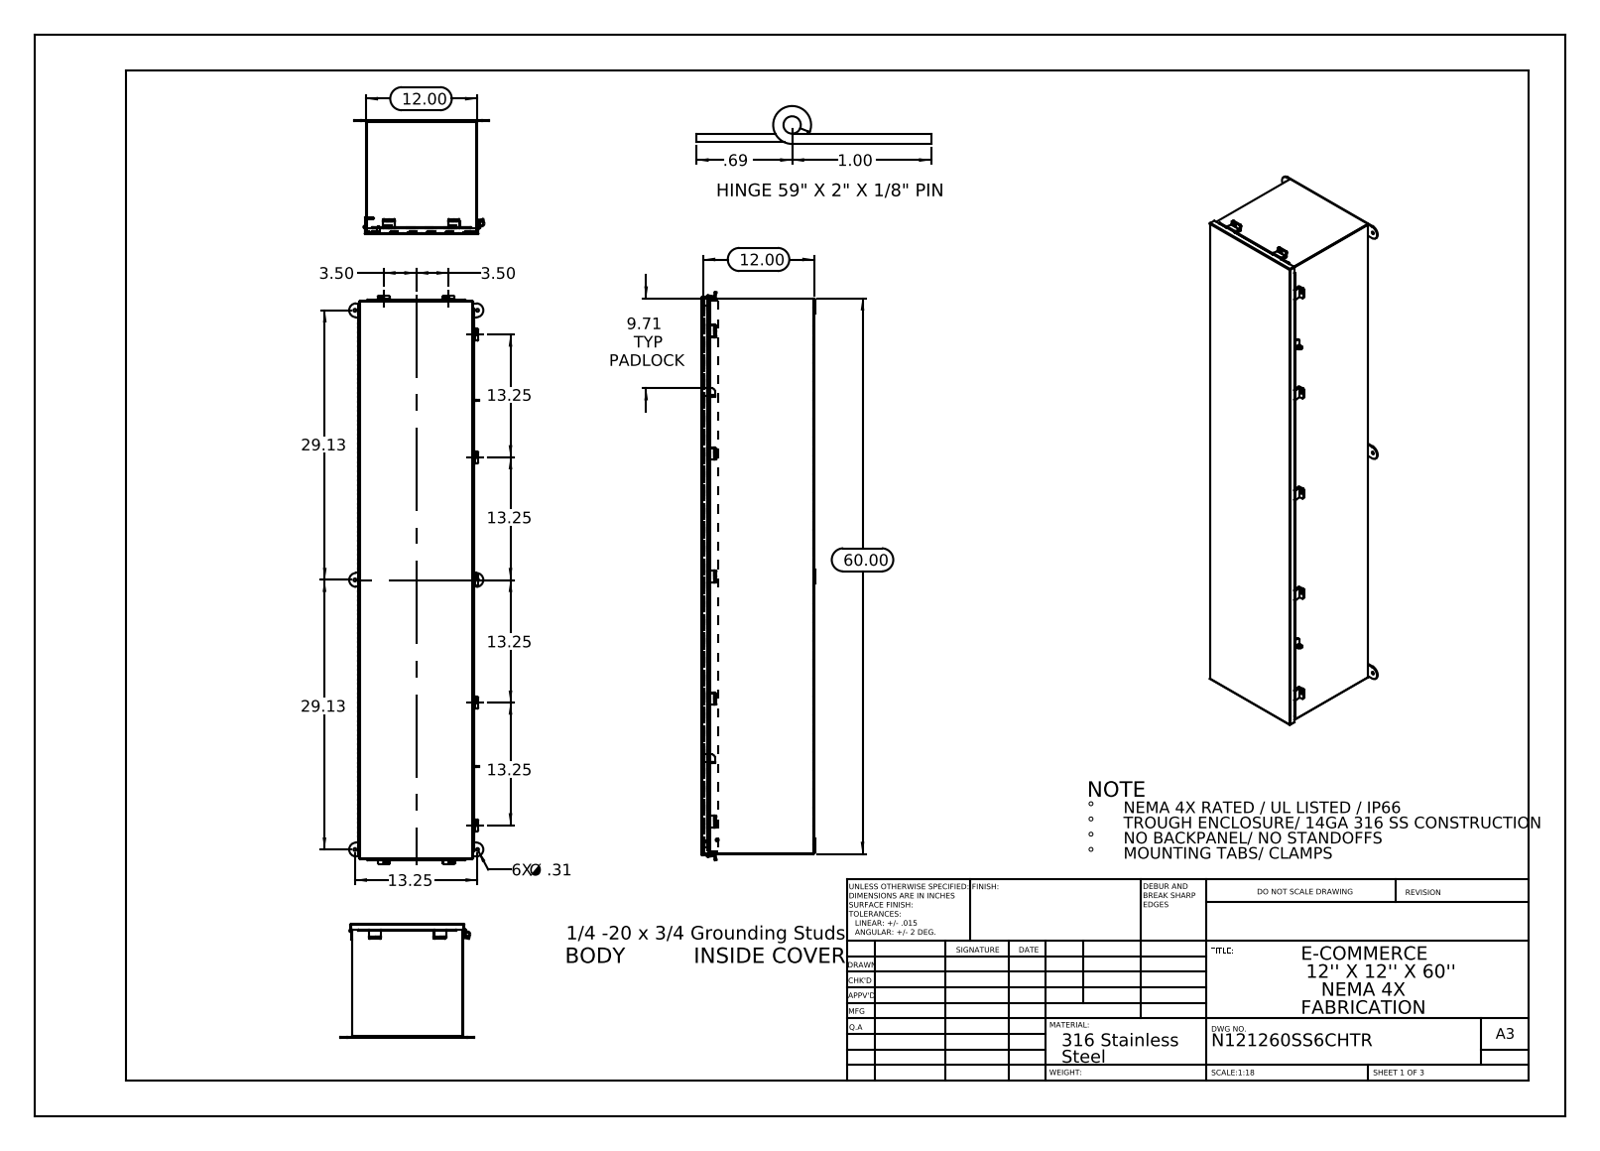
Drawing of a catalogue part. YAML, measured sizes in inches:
part_name: "N121260SSCHTR HW-CD-S-25020-034; N121260SSCHTR JIC Cover Clamp; N121260SSCHTR JIC Mounting Bracket; HW-CLH-JH-20154 (+8 more)"
step_written_by: "SolidWorks 2013 (CONFIG_CONTROL_DESIGN)"
units: inches
bodies: {solids: 31, faces: 1773, planar: 1066, cylindrical: 687, other: 20}
overall_size: [61.407, 14.5, 12.337]
volume: 266.4
surface_area: 7123
round_holes:
  - {diameter: 0.25, count: 9}
  - {diameter: 0.313, count: 6}
  - {diameter: 0.125, count: 1}
  - {diameter: 0.125, count: 1}
  - {diameter: 0.375, count: 1}
round_bosses_or_shafts:
  - {diameter: 0.315, count: 2}
  - {diameter: 0.236, count: 2}
  - {diameter: 0.273, count: 1}
  - {diameter: 0.25, count: 1}
partial_cylinders:
  - {radius: 0.125, count: 34}
  - {radius: 0.133, count: 18}
  - {radius: 0.009, count: 12}
  - {radius: 0.013, count: 10}
  - {radius: 0.088, count: 10}
  - {radius: 0.083, count: 6}
  - {radius: 0.1, count: 6}
  - {radius: 0.75, count: 6}
face_to_face_distances: [0.075, 11.925, 12.128, 12, 11.85, 12.203, 12.053, 59.925, 0.149, 12.074]
hole_center_spacings: [13.25, 29.125, 26.5, 7, 31.997, 31.998, 39.75, 58.25]
